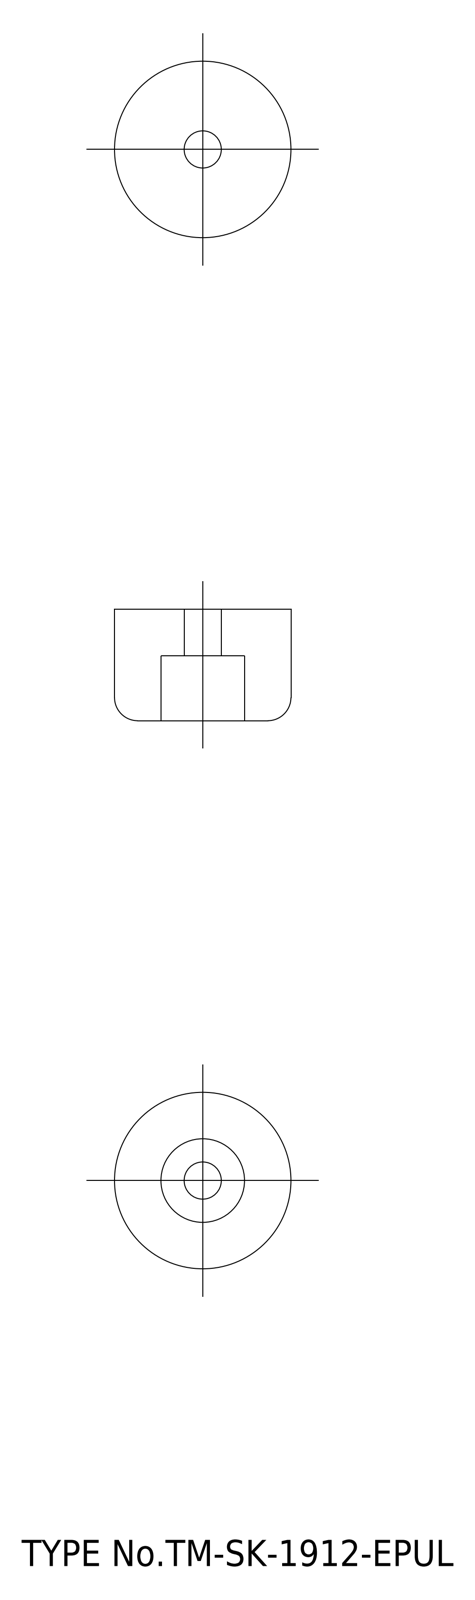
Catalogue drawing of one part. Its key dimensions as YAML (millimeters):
part_name: "washer; rubber foot"
step_written_by: "spGate 15.6.1 (AUTOMOTIVE_DESIGN)"
units: millimeters
bodies: {solids: 2, faces: 20, planar: 6, cylindrical: 12, other: 2}
overall_size: [19, 19, 12]
volume: 2819
surface_area: 1813
round_holes:
  - {diameter: 4, count: 1}
  - {diameter: 9, count: 1}
  - {diameter: 12, count: 1}
round_bosses_or_shafts:
  - {diameter: 19, count: 1}
face_to_face_distances: [4.2, 0.8, 5, 7, 7.8, 12]
